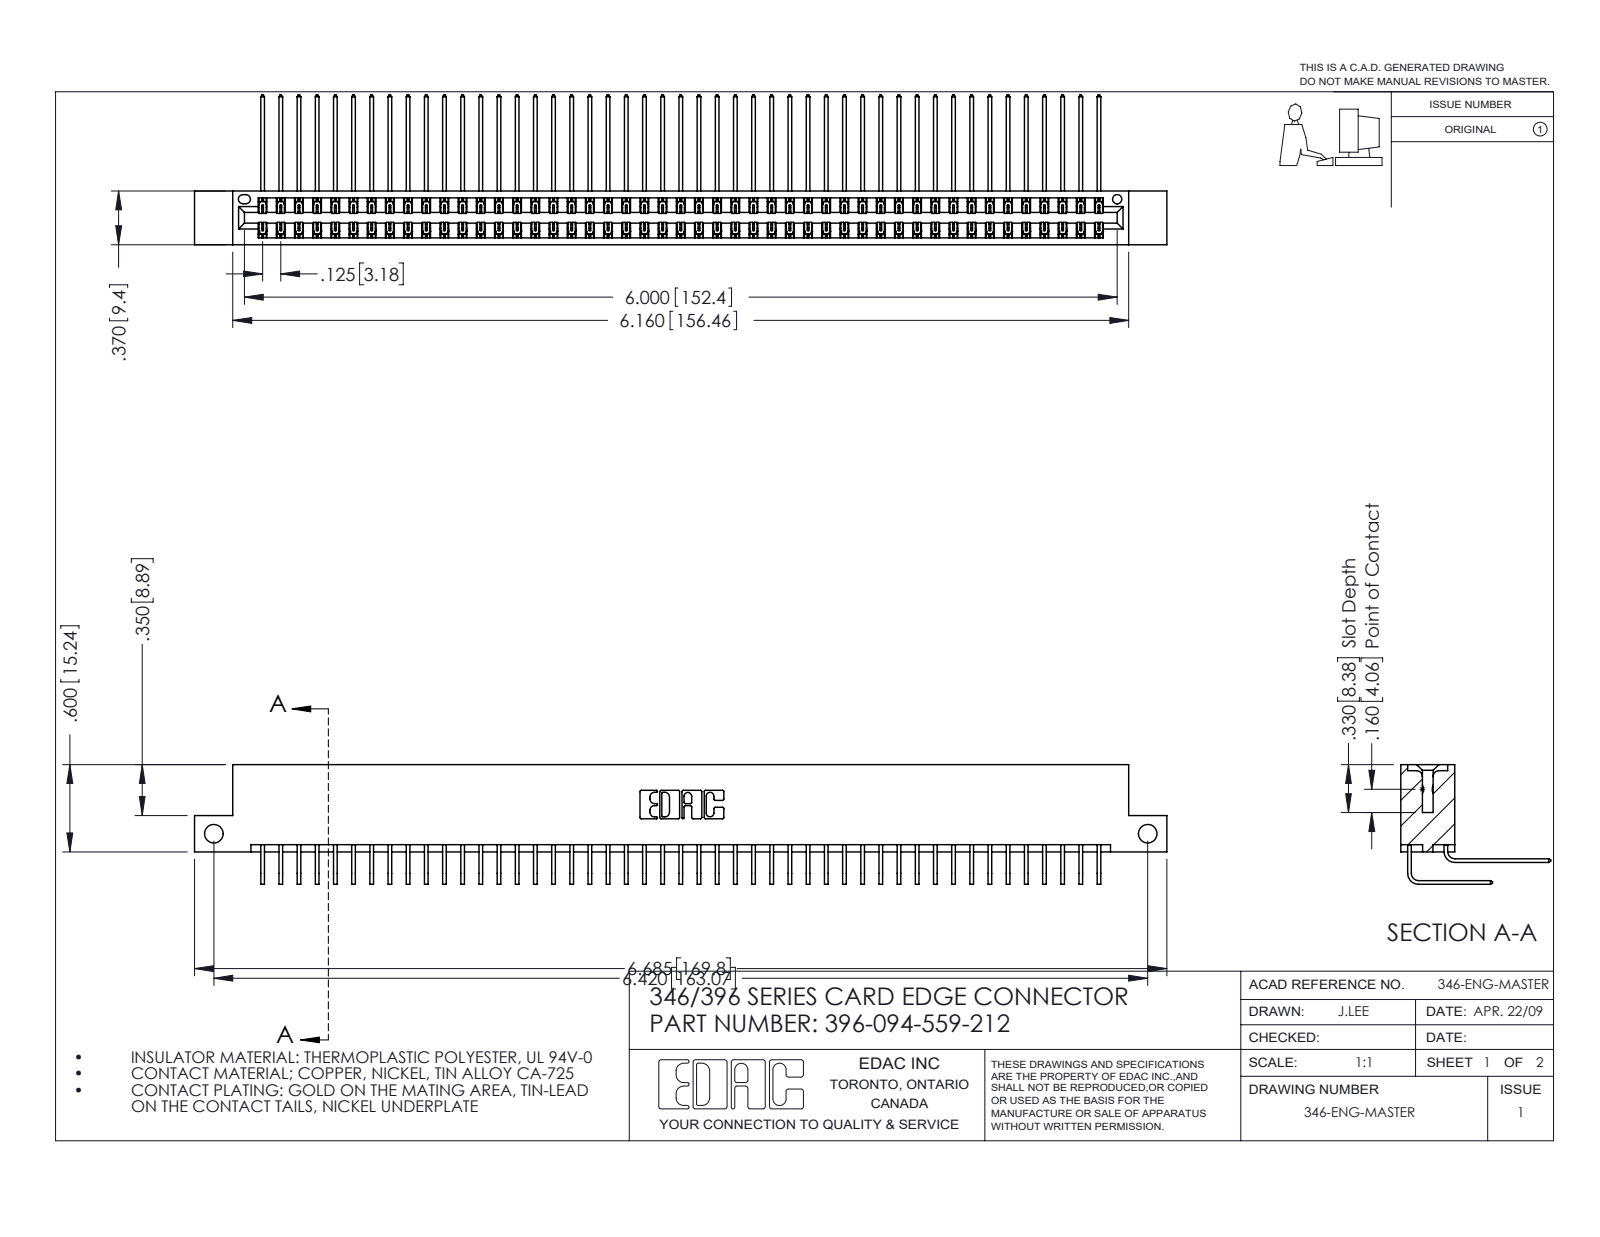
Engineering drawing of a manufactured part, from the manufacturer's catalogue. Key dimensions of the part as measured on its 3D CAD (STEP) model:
Part name (STEP PRODUCT): 345-292-001_559 Tail - 2; 346 Part_Flush Mounting Lugs - Side Mount; 345-292-001_558 559 Tail - 1; 396-094-559-212
STEP written by: SolidWorks 2016 (CONFIG_CONTROL_DESIGN)
Units: inches
Bodies: 95 solids, 5198 faces (3554 planar, 1644 cylindrical, 0 other)
Overall size (bounding box): 6.685 × 1.03 × 0.823
Volume: 1.041 in³ · Surface area: 40.27 in²
Round holes (diameter × count): ⌀0.128 ×2, ⌀0.064 ×1
Partial cylindrical surfaces — rounded edges, fillets, slot ends (radius × count): R0.006 ×141, R0.01 ×22, R0.007 ×6, R0.031 ×6, R0.026 ×3, R0.014 ×2, R0.022 ×2, R0.024 ×2
Main face-to-face distances: 0.048, 0.322, 0.025, 0.37, 0.25, 0.072, 0.298, 0.275, 0.148, 0.222
Hole centre spacings: 6.42
